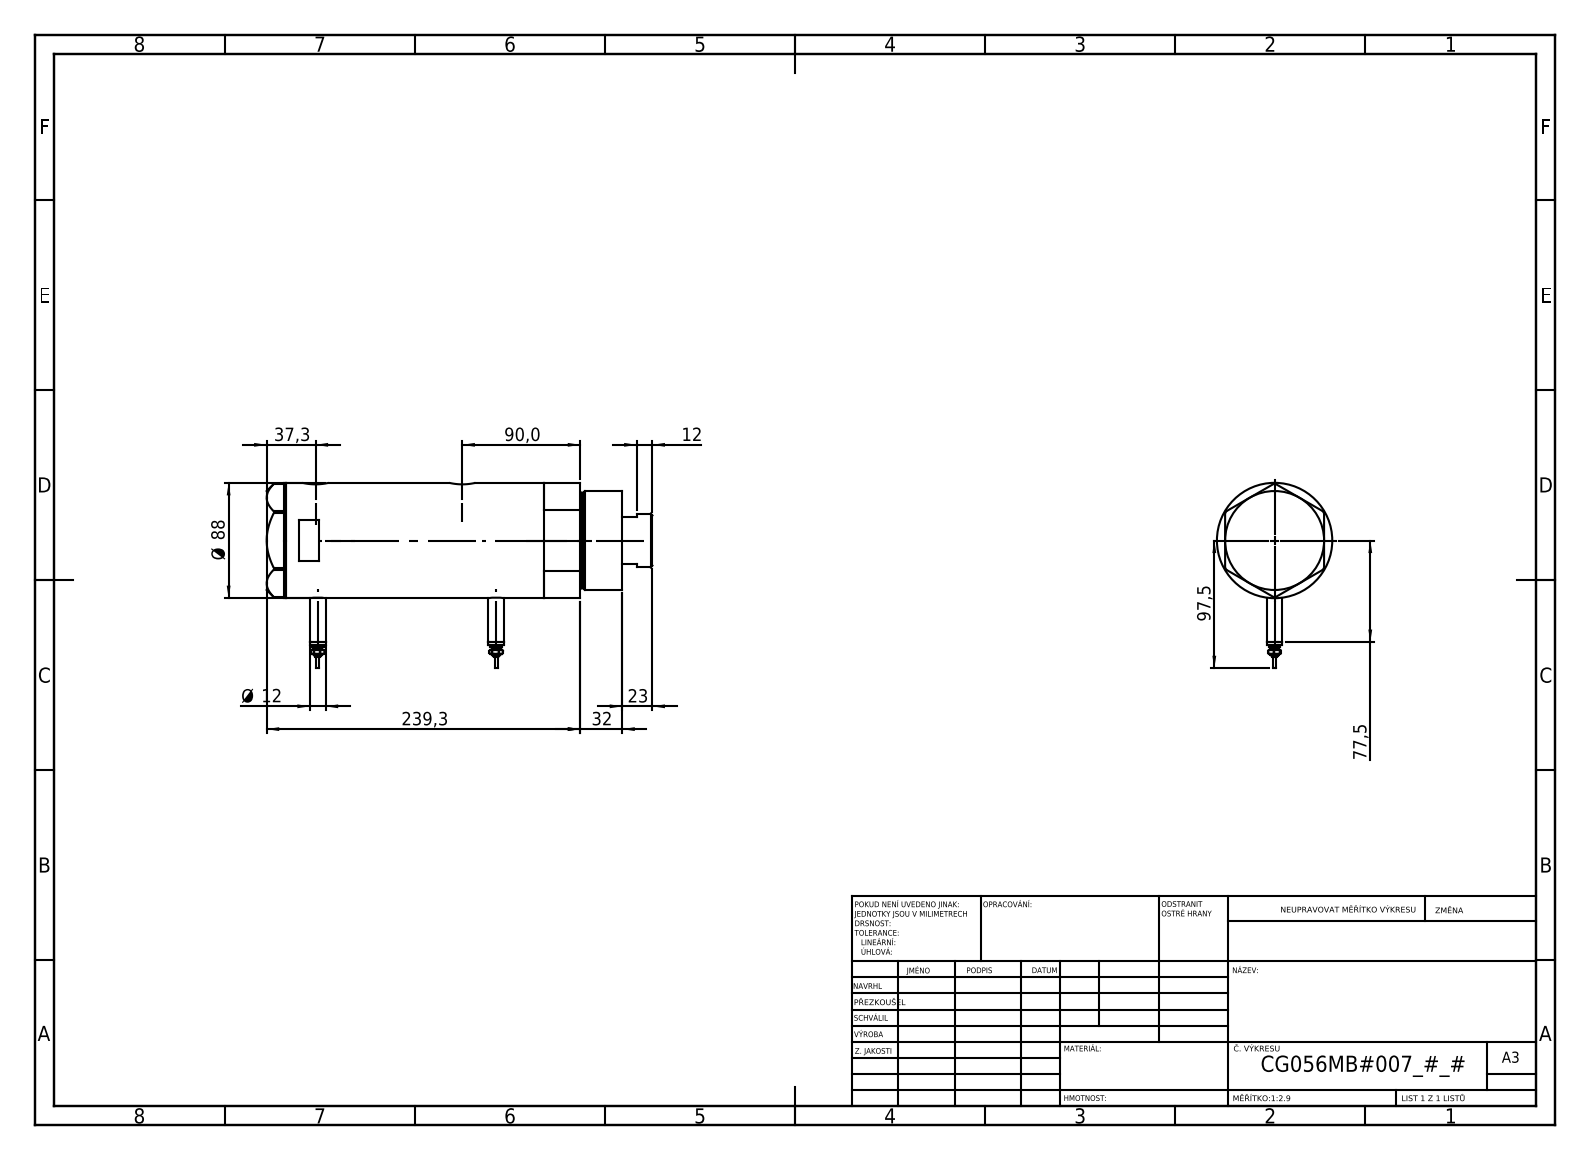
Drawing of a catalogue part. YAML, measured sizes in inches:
part_name: "V270CG_FRONT; V270CG_VC; V270CG_BACK; V270CG_MIDDLE (+1 more)"
step_written_by: "SolidWorks 2019 (CONFIG_CONTROL_DESIGN)"
units: inches
bodies: {solids: 6, faces: 213, planar: 80, cylindrical: 69, other: 64}
overall_size: [11.587, 5.571, 3.465]
volume: 95.38
surface_area: 349.5
round_holes:
  - {diameter: 0.492, count: 2}
  - {diameter: 0.518, count: 2}
  - {diameter: 0.787, count: 2}
  - {diameter: 0.571, count: 1}
  - {diameter: 1.654, count: 1}
  - {diameter: 1.713, count: 1}
  - {diameter: 2.205, count: 1}
  - {diameter: 2.362, count: 1}
  - {diameter: 3.15, count: 1}
round_bosses_or_shafts:
  - {diameter: 0.472, count: 2}
  - {diameter: 0.354, count: 2}
  - {diameter: 0.276, count: 2}
  - {diameter: 0.177, count: 2}
  - {diameter: 0.098, count: 2}
  - {diameter: 3.465, count: 1}
  - {diameter: 2.953, count: 1}
  - {diameter: 2.874, count: 1}
face_to_face_distances: [5.291, 1.024, 4.268, 0.591, 1.614, 5.882, 10.091, 10.681, 9.067, 4.799]
hole_center_spacings: [0.067, 1.016, 4.343, 4.409, 5.358, 5.425]
